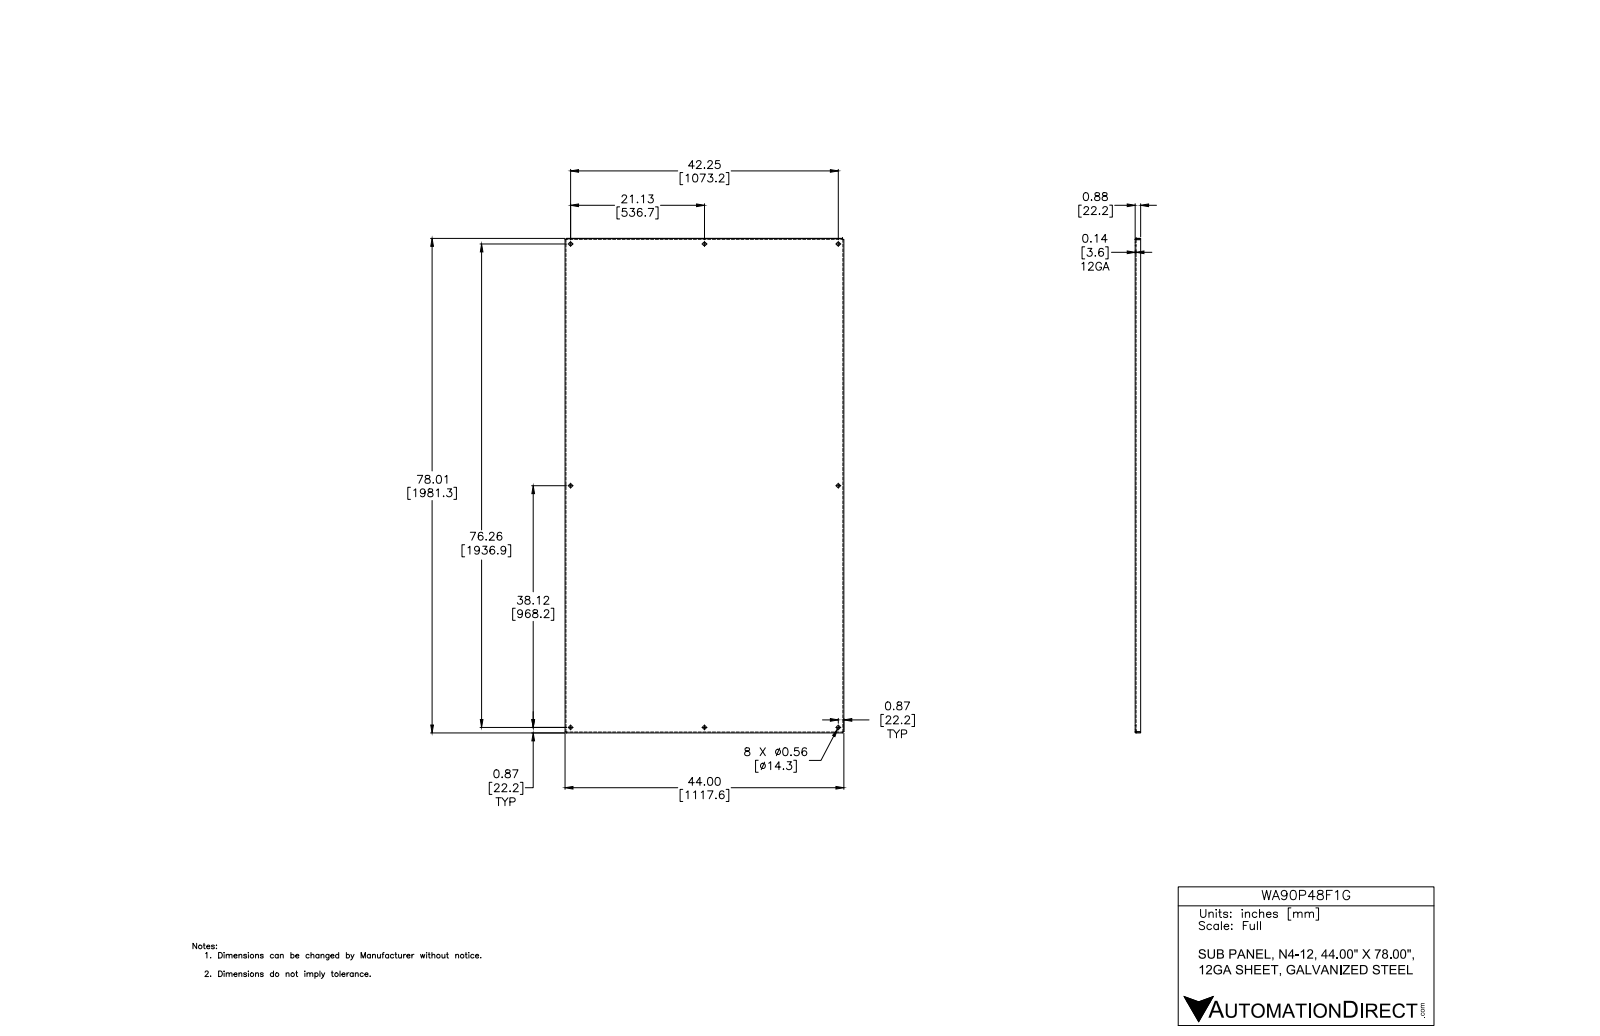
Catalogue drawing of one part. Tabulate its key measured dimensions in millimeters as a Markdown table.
| quantity | value |
| --- | --- |
| part name | WA_P_F_G |
| STEP written by | Autodesk Inventor 2012 (AUTOMOTIVE_DESIGN) |
| units | millimeters |
| bodies | 1 solid, 46 faces (22 planar, 16 cylindrical, 8 other) |
| overall size | 1981.2 × 1117.6 × 22.2 |
| volume | 7 381 000 mm³ |
| surface area | 4 671 000 mm² |
| round holes (diameter × count) | 14.3 × 8 |
| partial cylindrical surfaces (radius × count) | 0.4 × 4, 3.6 × 4 |
| main face-to-face distances | 3.2, 3.2, 1114.4, 1117.6, 1111.3, 1978, 1981.2, 1974.9, 1978, 19.1 |
| hole center spacings | 1107.1, 536.6, 536.6, 968.4, 968.4, 1073.2, 1445.5, 1936.8 |
